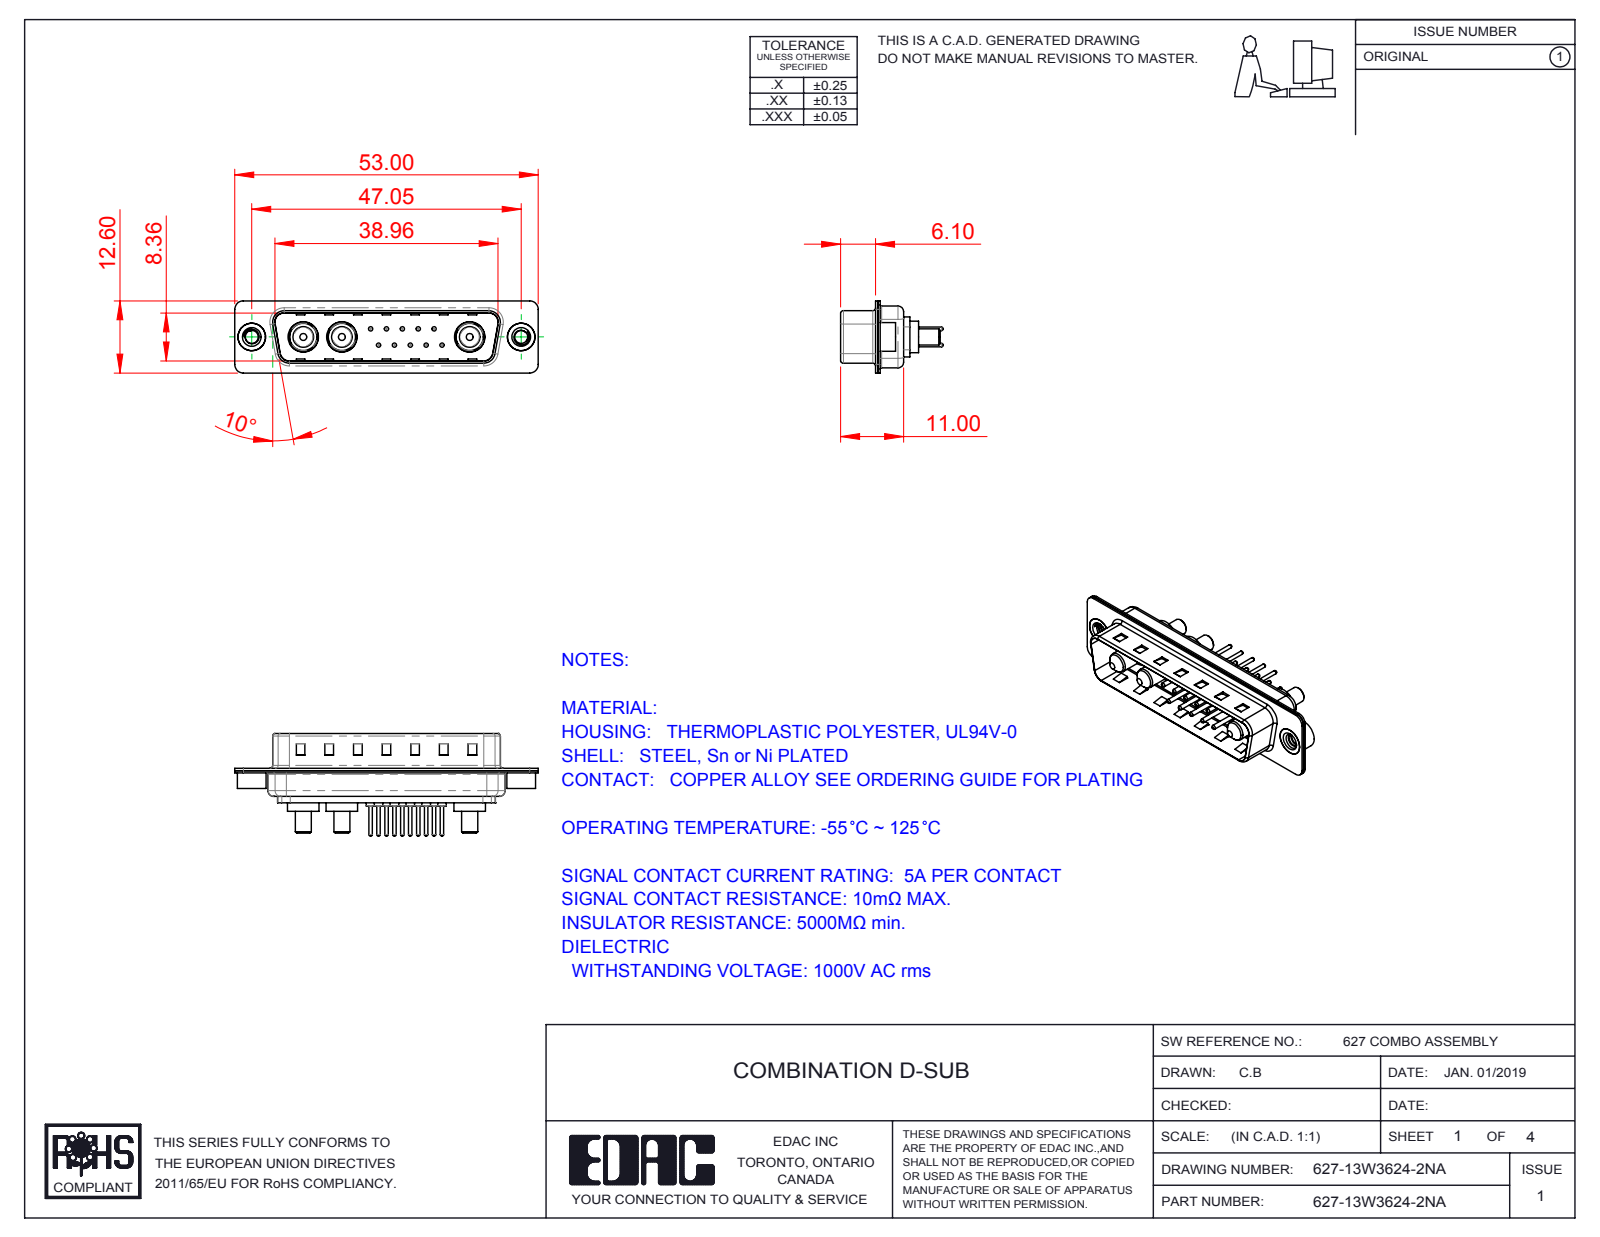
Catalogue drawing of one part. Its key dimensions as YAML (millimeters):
part_name: "Power Pin_20A S; 627-13W3624-2NA; 627Combo Housing_13W3; 627Combo Threaded Rivet_A (+5 more)"
step_written_by: "SolidWorks 2016 (CONFIG_CONTROL_DESIGN)"
units: millimeters
bodies: {solids: 21, faces: 865, planar: 271, cylindrical: 335, other: 259}
overall_size: [53, 17.9, 12.6]
volume: 2926
surface_area: 6748
round_holes:
  - {diameter: 0.75, count: 10}
  - {diameter: 1.6, count: 10}
  - {diameter: 2, count: 10}
  - {diameter: 4.85, count: 3}
  - {diameter: 5.3, count: 3}
  - {diameter: 2.26, count: 2}
  - {diameter: 4, count: 2}
  - {diameter: 4.8, count: 2}
round_bosses_or_shafts:
  - {diameter: 1.5, count: 10}
  - {diameter: 0.6, count: 10}
  - {diameter: 5.5, count: 3}
  - {diameter: 5.2, count: 3}
  - {diameter: 4.75, count: 3}
  - {diameter: 3.75, count: 3}
  - {diameter: 3.6, count: 3}
  - {diameter: 2.8, count: 3}
partial_cylinders:
  - {radius: 1.5, count: 16}
  - {radius: 2, count: 12}
  - {radius: 0.5, count: 8}
  - {radius: 1.6, count: 8}
  - {radius: 0.25, count: 4}
  - {radius: 0.6, count: 4}
  - {radius: 0.65, count: 4}
  - {radius: 0.9, count: 4}
face_to_face_distances: [0.4, 0.82, 9.58, 8.76, 1.5, 5.6, 0.8, 5.2, 1.22, 9.98]
hole_center_spacings: [3.16, 2.77, 5.04, 5.54, 7.49, 5.03, 8.31, 10.11]
